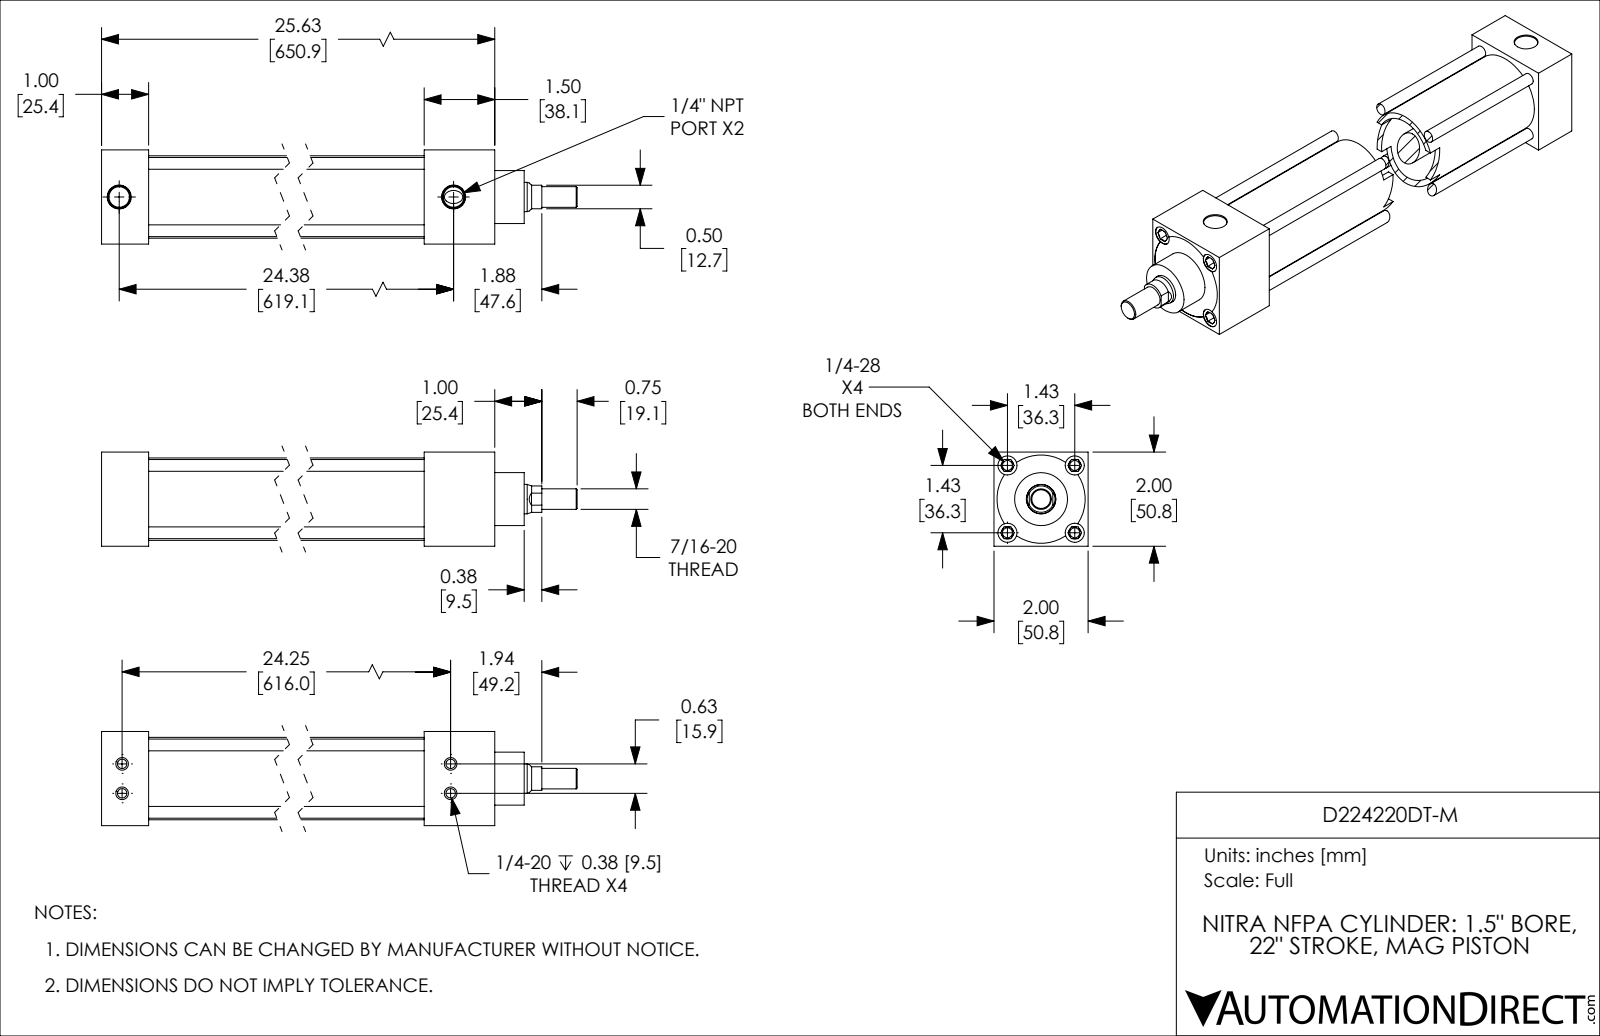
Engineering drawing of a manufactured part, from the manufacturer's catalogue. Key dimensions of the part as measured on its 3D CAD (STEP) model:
Part name (STEP PRODUCT): D224220DT-M_BODY; D224220DT-M_PISTON_KK1; D224220DT-M
STEP written by: SolidWorks 2019 (CONFIG_CONTROL_DESIGN)
Units: inches
Bodies: 2 solids, 203 faces (58 planar, 65 cylindrical, 80 other)
Overall size (bounding box): 27.375 × 2 × 2
Volume: 38.27 in³ · Surface area: 414.3 in²
Round holes (diameter × count): ⌀0.201 ×4, ⌀0.213 ×4, ⌀0.406 ×4, ⌀0.438 ×2, ⌀0.626 ×1, ⌀1.501 ×1
Round bosses / shafts (diameter × count): ⌀0.25 ×4, ⌀1.751 ×1, ⌀1.499 ×1, ⌀1.125 ×1, ⌀0.624 ×1, ⌀0.437 ×1
Partial cylindrical surfaces — rounded edges, fillets, slot ends (radius × count): R0.281 ×1, R0.937 ×1
Main face-to-face distances: 2, 1, 24.125, 23.125, 25.62, 24.62, 1.495, 1.125, 2.125, 22
Hole centre spacings: 0.319, 1.011, 1.43, 0.625, 2.022, 24.25, 24.258, 24.314
